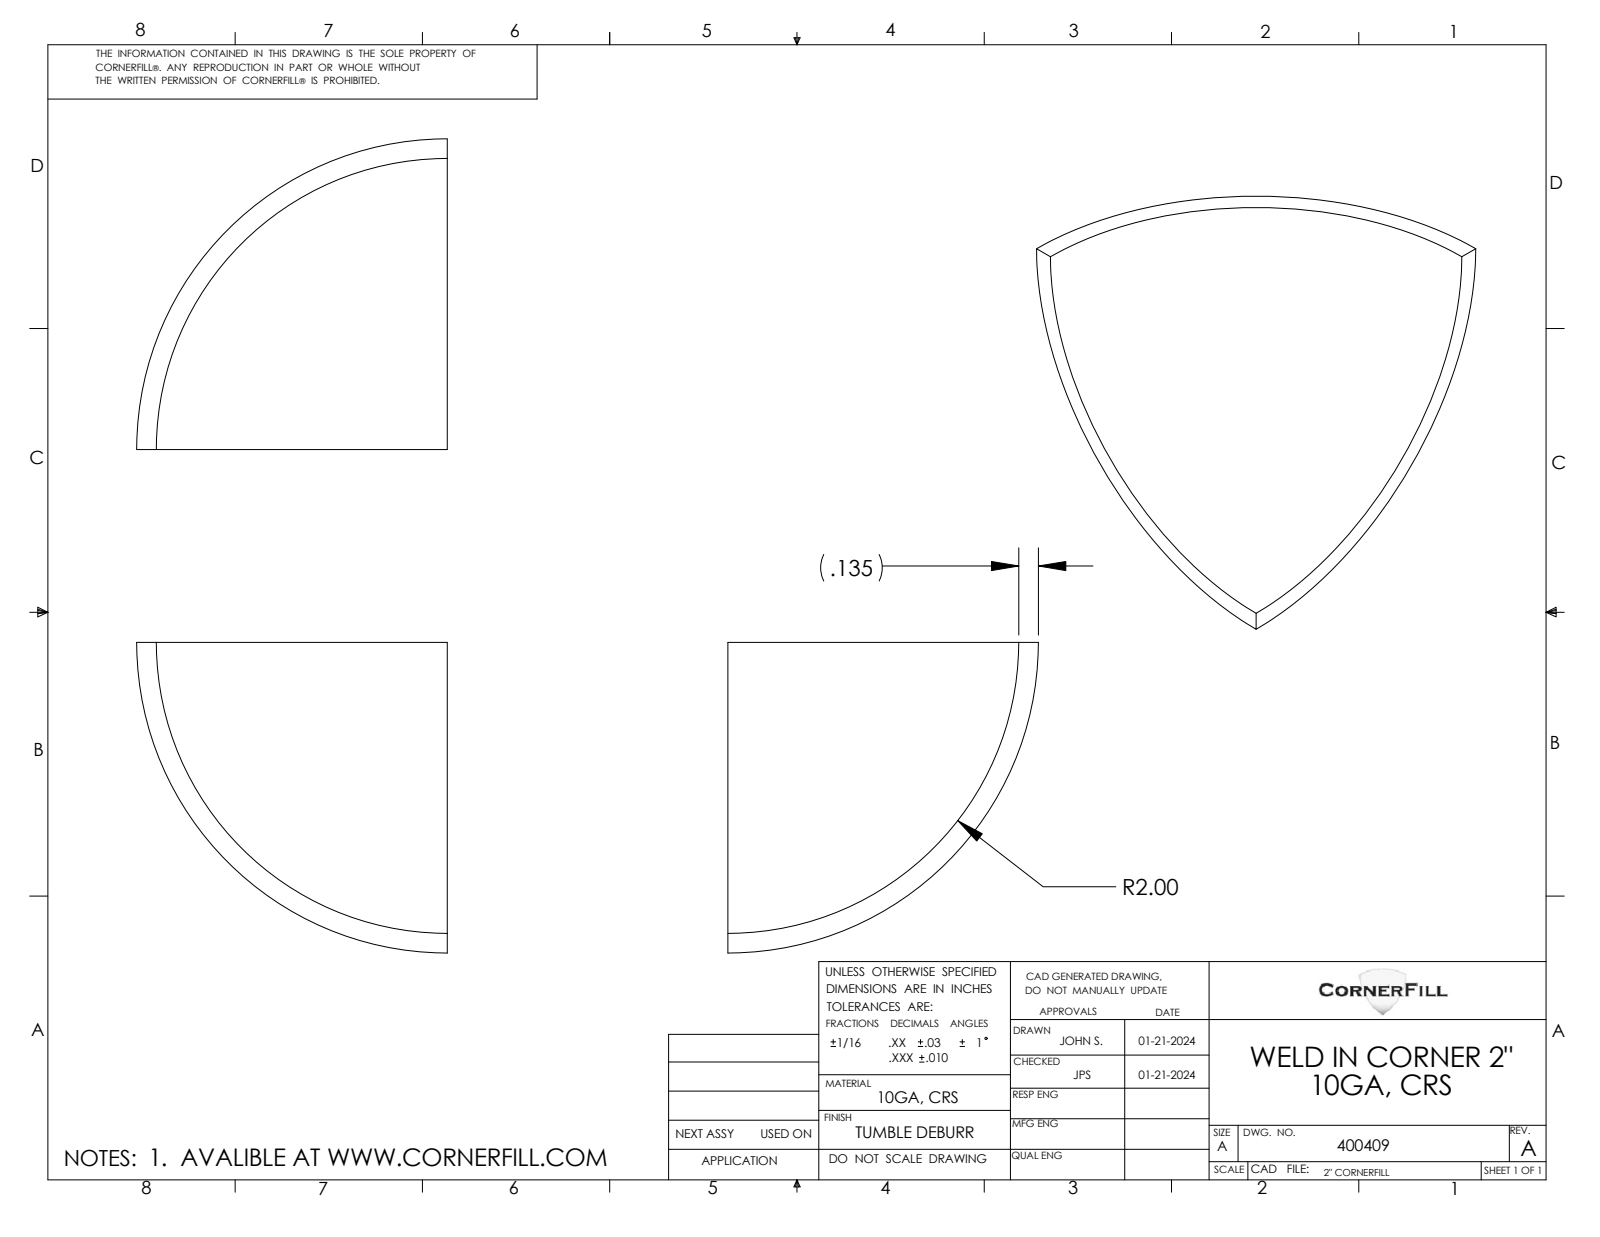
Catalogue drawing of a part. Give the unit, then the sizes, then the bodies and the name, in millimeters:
Units: millimetres
Overall size (bounding box): 76.7 × 54.2 × 54.2
Volume: 14 900 mm³ · Surface area: 9 523 mm²
Bodies: 1 solid, 5 faces (3 planar, 0 cylindrical, 2 other)
Part name (STEP PRODUCT): 400409
STEP written by: SolidWorks 2021 (CONFIG_CONTROL_DESIGN)
